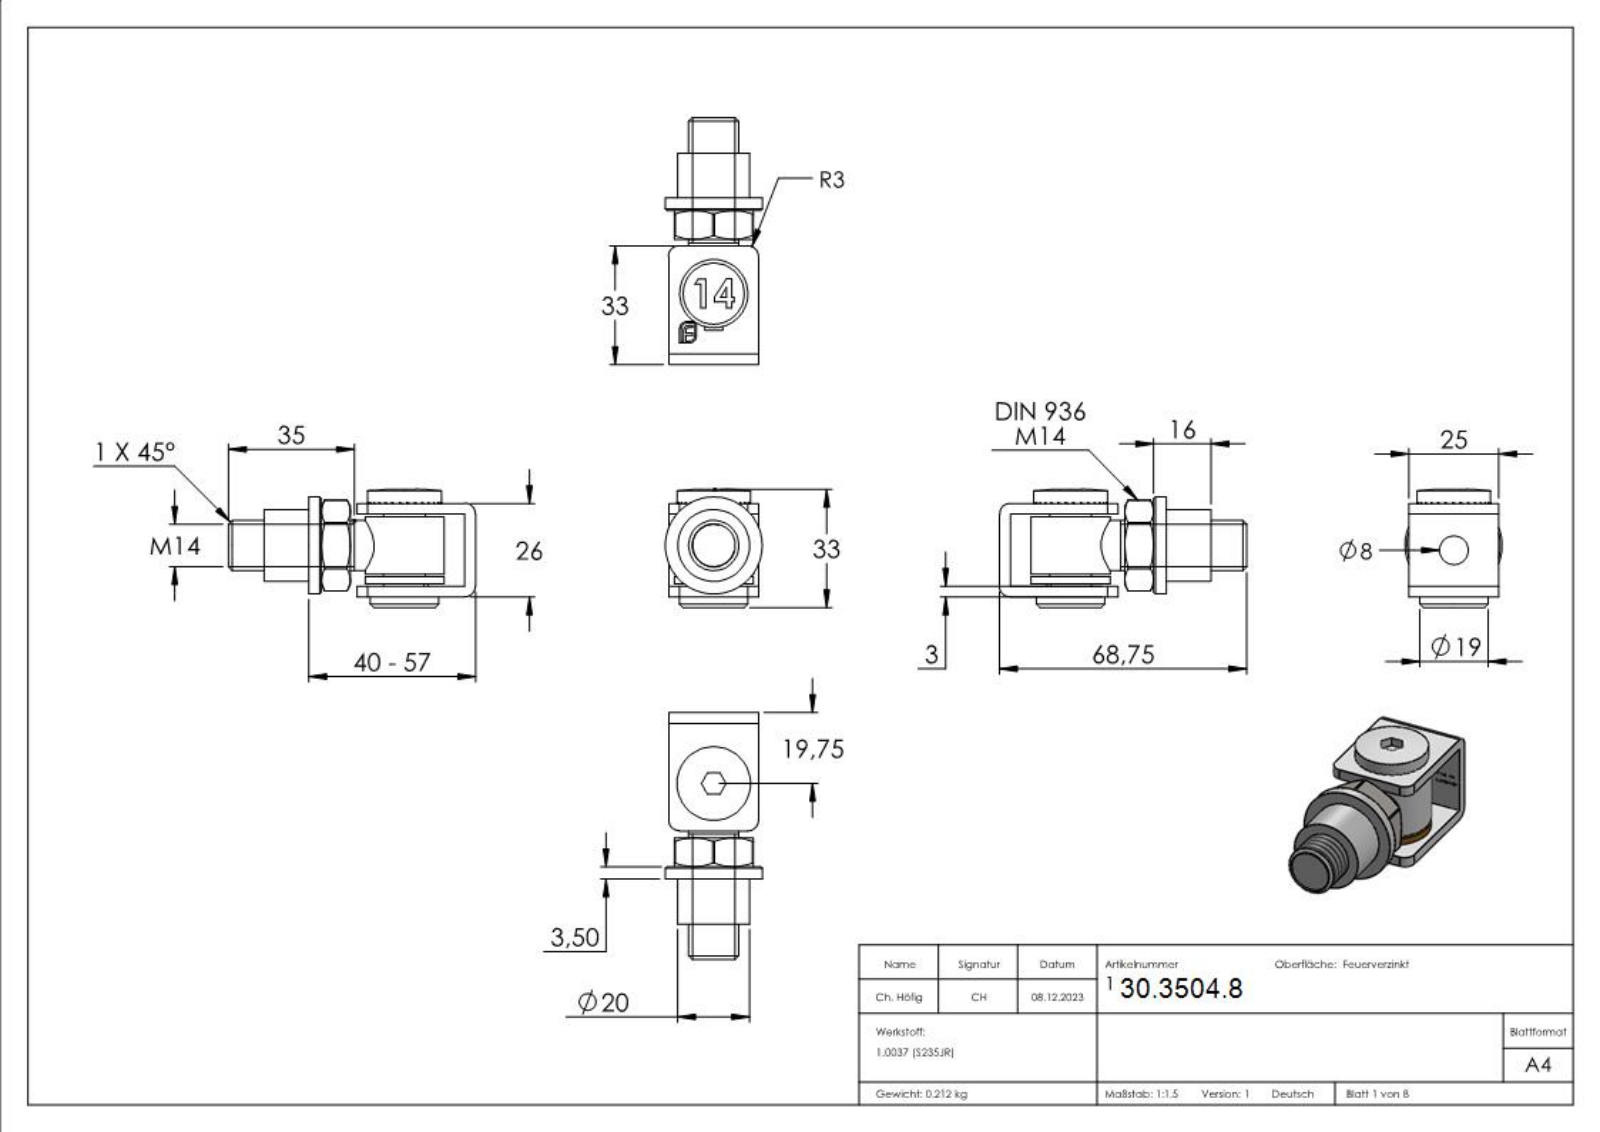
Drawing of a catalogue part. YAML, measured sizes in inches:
part_name: "Torband Teil6_120-M14-FEV Teil6; Torband Teil2_120-M14-FEV Teil2; Torband Teil5_120-M14-FEV Teil5; 120-M14-FEV (+4 more)"
step_written_by: "SolidWorks 2018 (CONFIG_CONTROL_DESIGN)"
units: inches
bodies: {solids: 7, faces: 519, planar: 363, cylindrical: 29, other: 127}
overall_size: [2.707, 1.298, 1.063]
volume: 1.654
surface_area: 25.66
round_holes:
  - {diameter: 0.197, count: 1}
  - {diameter: 0.315, count: 1}
  - {diameter: 0.472, count: 1}
  - {diameter: 0.492, count: 1}
round_bosses_or_shafts:
  - {diameter: 1.063, count: 1}
  - {diameter: 0.866, count: 1}
  - {diameter: 0.807, count: 1}
  - {diameter: 0.787, count: 1}
  - {diameter: 0.748, count: 1}
  - {diameter: 0.551, count: 1}
  - {diameter: 0.461, count: 1}
  - {diameter: 0.236, count: 1}
partial_cylinders:
  - {radius: 0.02, count: 6}
  - {radius: 0.118, count: 4}
face_to_face_distances: [0.118, 0.906, 1.024, 0.787, 0.144, 0.879, 0.026, 0.761, 1.688, 1.57]
hole_center_spacings: [0.052]
